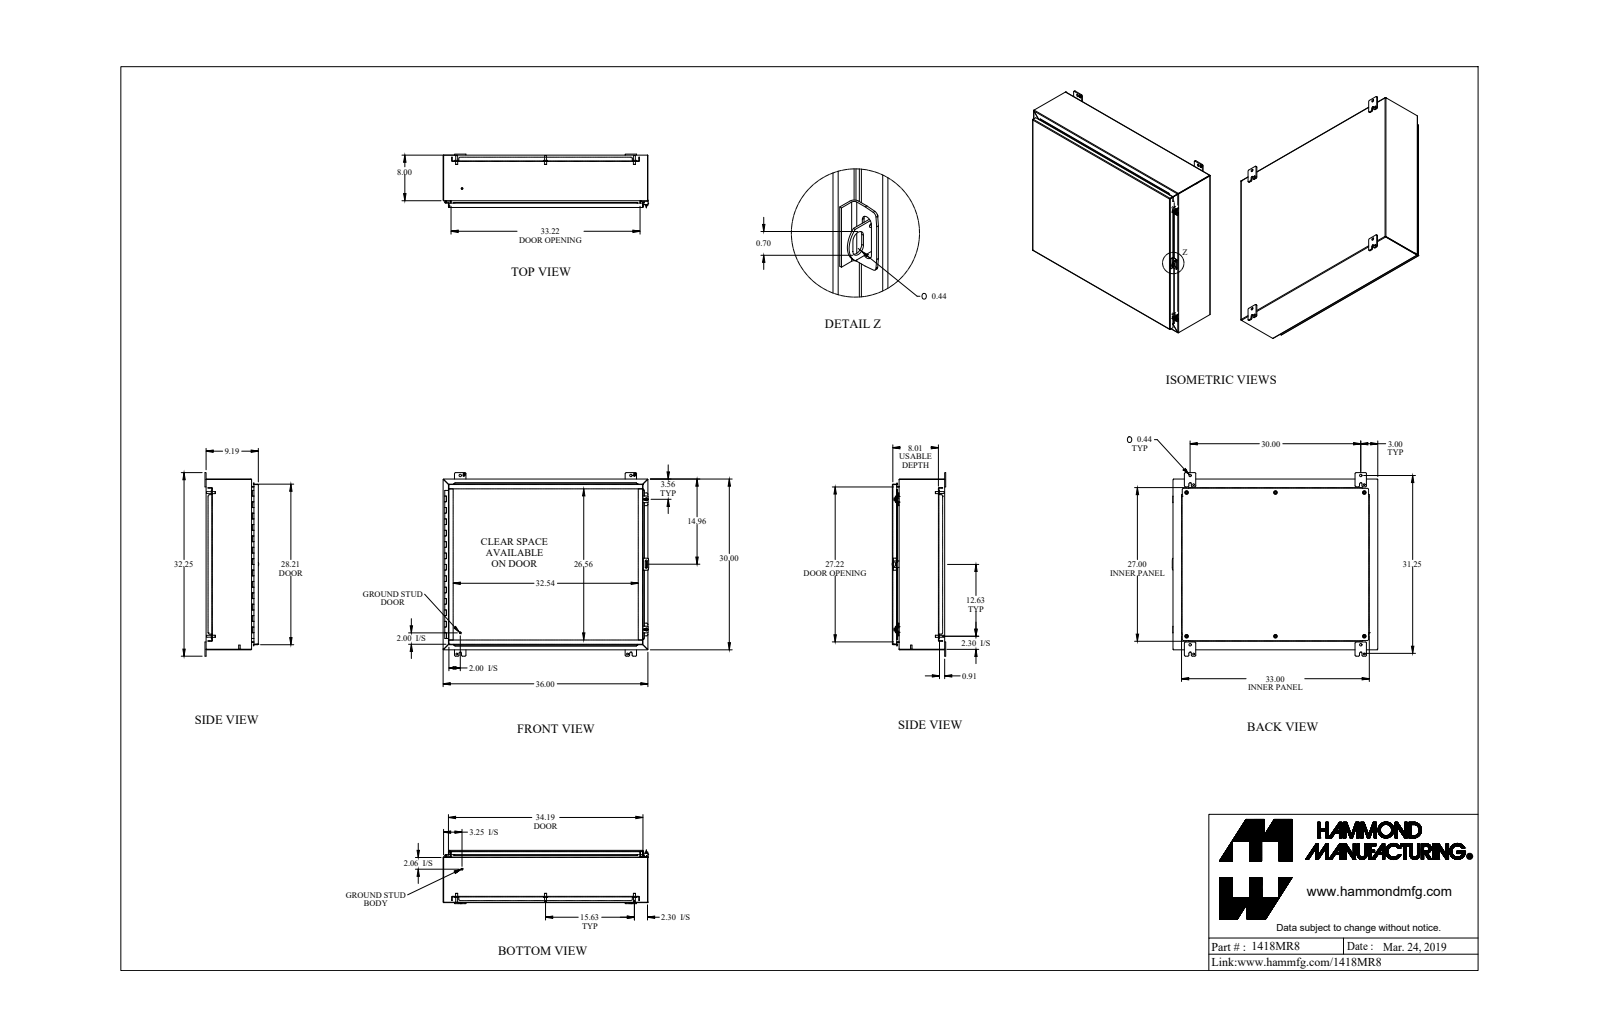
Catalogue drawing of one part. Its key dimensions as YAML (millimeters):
part_name: "1418MR8_Default"
step_written_by: "SolidWorks 2019 (CONFIG_CONTROL_DESIGN)"
units: millimeters
bodies: {solids: 47, faces: 1383, planar: 829, cylindrical: 470, other: 84}
overall_size: [917.6, 819.2, 239.7]
volume: 6332000
surface_area: 6444000
round_holes:
  - {diameter: 12.7, count: 6}
  - {diameter: 7.8, count: 4}
  - {diameter: 8, count: 4}
  - {diameter: 11.1, count: 4}
  - {diameter: 11.3, count: 4}
  - {diameter: 5.4, count: 2}
  - {diameter: 6.7, count: 2}
  - {diameter: 9.5, count: 2}
  - {diameter: 3.2, count: 1}
  - {diameter: 4.7, count: 1}
round_bosses_or_shafts:
  - {diameter: 16.5, count: 6}
  - {diameter: 9.5, count: 6}
  - {diameter: 8.4, count: 6}
  - {diameter: 25.4, count: 4}
  - {diameter: 12.7, count: 2}
  - {diameter: 9.9, count: 2}
  - {diameter: 7.1, count: 2}
  - {diameter: 6.4, count: 2}
partial_cylinders:
  - {radius: 4.8, count: 26}
  - {radius: 0.9, count: 24}
  - {radius: 2.7, count: 24}
  - {radius: 6.4, count: 16}
  - {radius: 1.2, count: 13}
  - {radius: 3.6, count: 13}
  - {radius: 2.9, count: 12}
  - {radius: 4.7, count: 12}
face_to_face_distances: [1.8, 231.5, 229.6, 233.3, 2.4, 23.8, 25.6, 205.3, 203.4, 26.2]
hole_center_spacings: [641.4, 44.1, 396.9, 754.2, 755.7, 762, 1073.2, 77.9]
